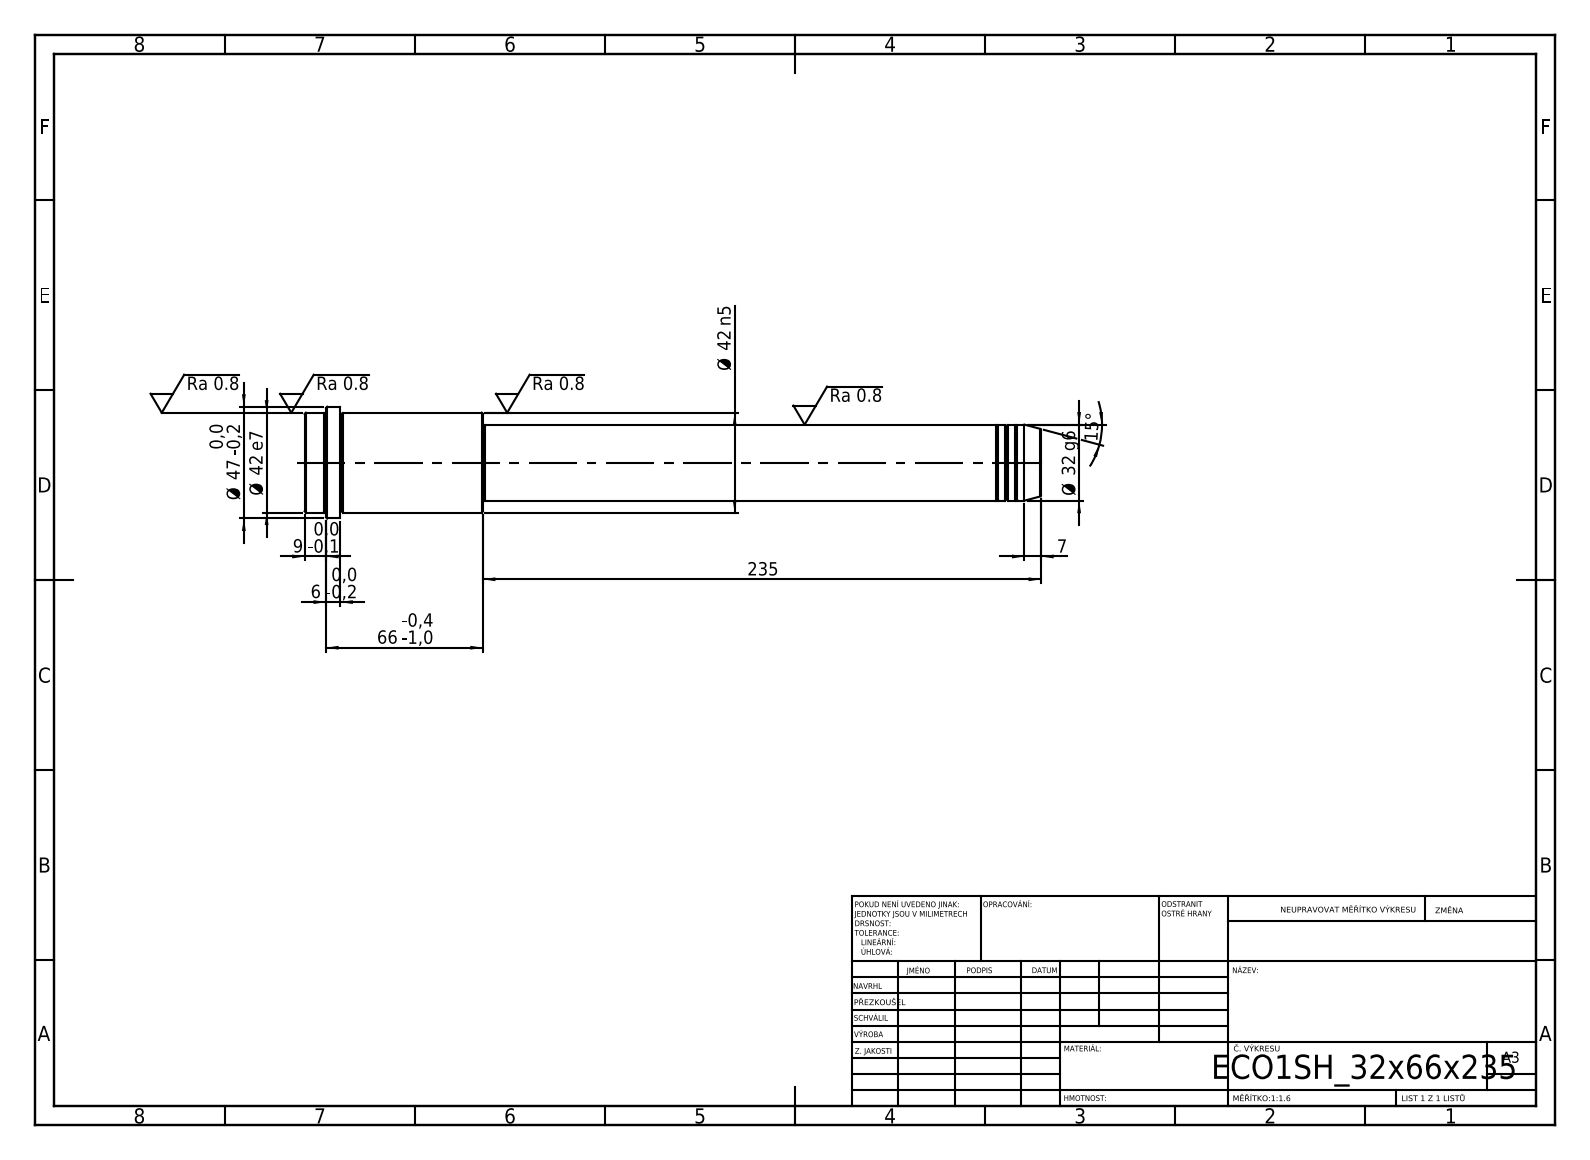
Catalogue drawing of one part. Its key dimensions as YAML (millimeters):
step_written_by: "SolidWorks 2019 (CONFIG_CONTROL_DESIGN)"
units: millimeters
bodies: {solids: 1, faces: 52, planar: 6, cylindrical: 16, other: 30}
overall_size: [310, 47, 47]
volume: 294047
surface_area: 37161
round_bosses_or_shafts:
  - {diameter: 47, count: 1}
  - {diameter: 42, count: 1}
  - {diameter: 32, count: 1}
  - {diameter: 31, count: 1}
face_to_face_distances: [310, 235, 75, 295, 60, 15, 301, 66, 6, 9]
